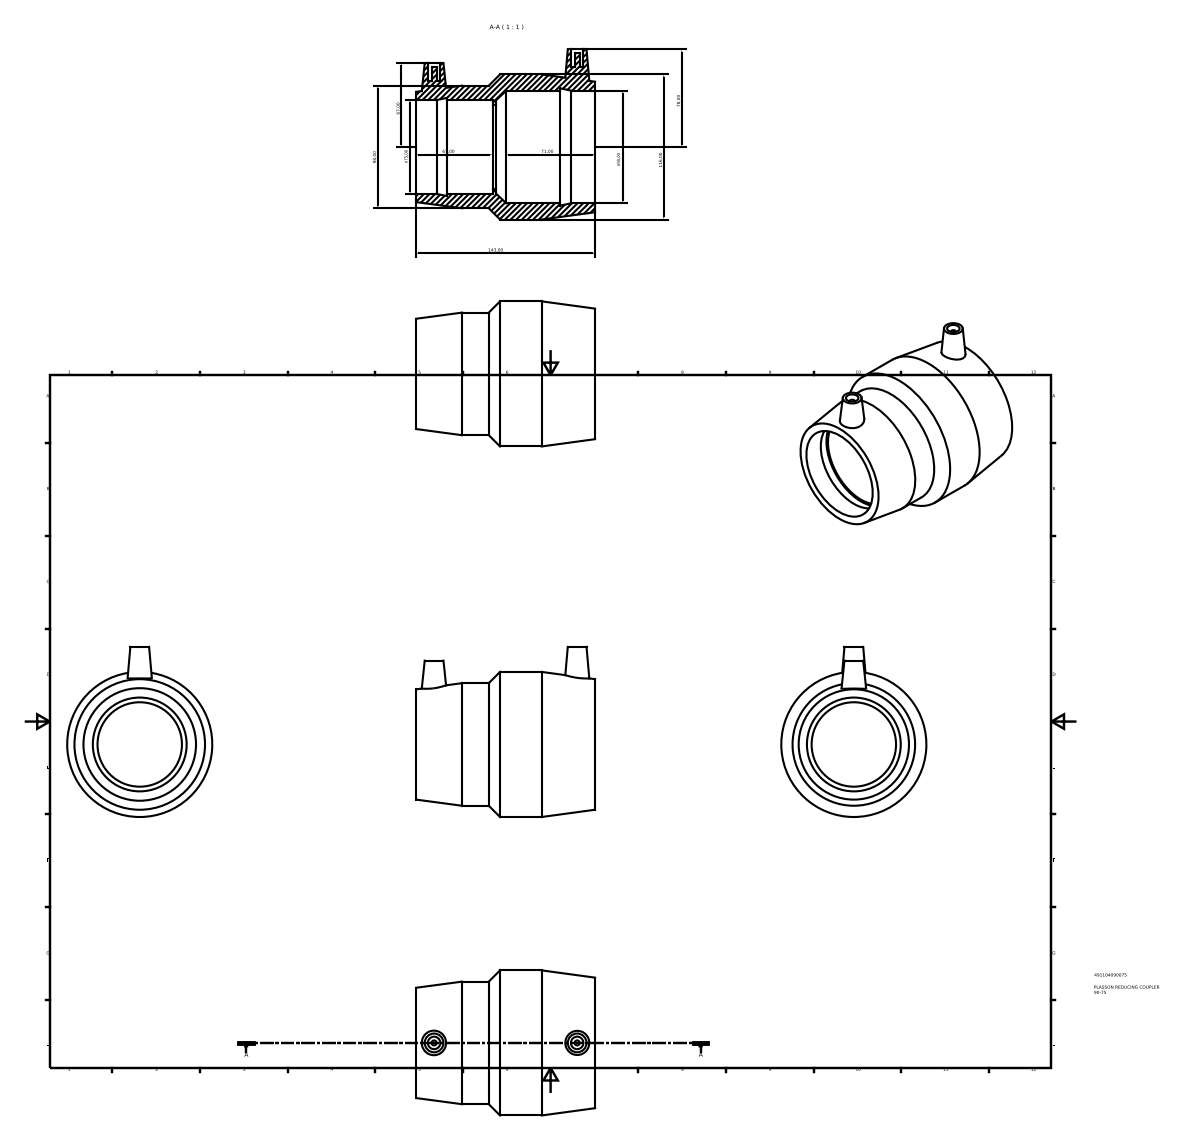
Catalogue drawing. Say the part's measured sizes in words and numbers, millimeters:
The part is named "491104090075". Its 3-D file was written by "Autodesk Inventor 2015 (AUTOMOTIVE_DESIGN)". It is 1 solid with 31 faces: 12 planar, 11 cylindrical and 8 other. Overall it measures 143 by 136 by 116 millimeters. Its volume is 481 034 cubic millimeters and its surface area 96 823 square millimeters. Round holes: 2 of diameter 10, 1 of diameter 67.5, 1 of diameter 75, 1 of diameter 90. Round bosses or shafts: 2 of diameter 4, 1 of diameter 116, 1 of diameter 98. The main face-to-face distances are 143, 64.05, 78.95, 61, 3.05, 82, 114.6, 53.6, 50.55, 28.4. The hole center spacings are 114.4.
